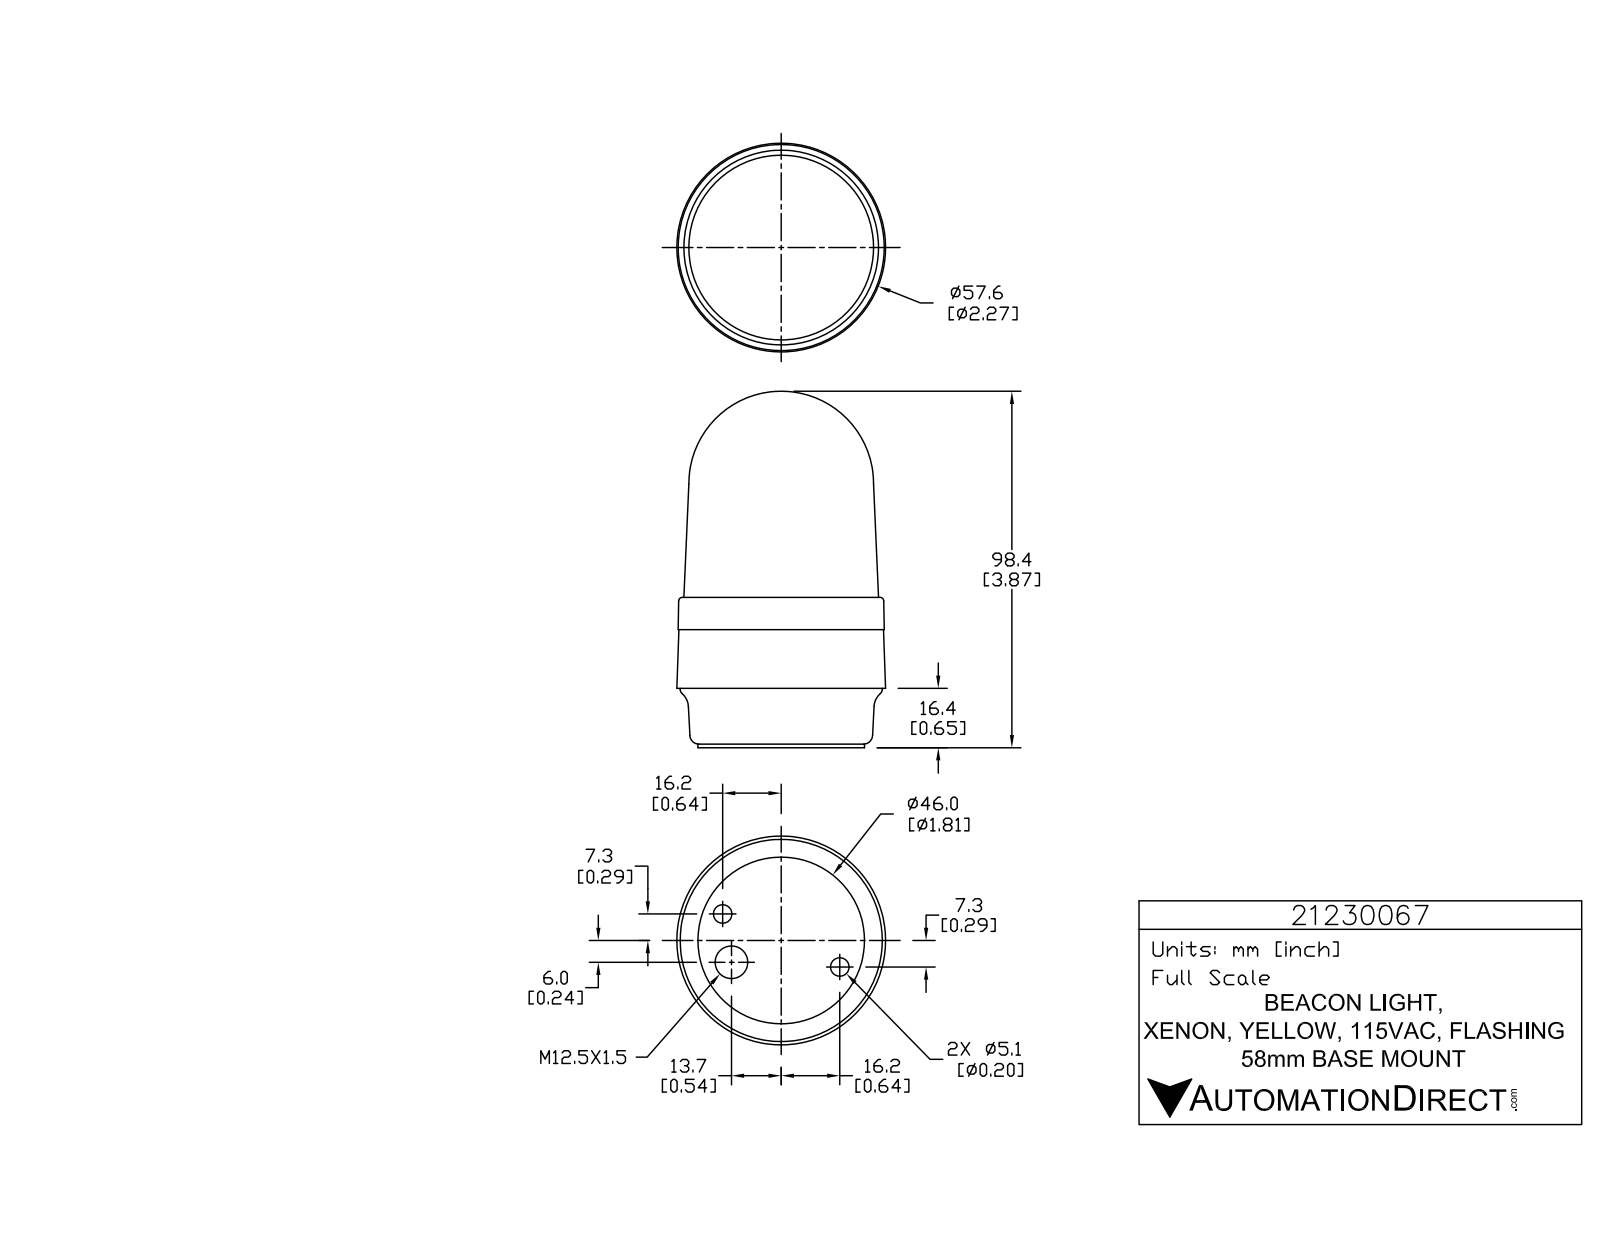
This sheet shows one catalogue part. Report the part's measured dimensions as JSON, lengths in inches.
{"part_name": "21230067", "step_written_by": "SolidWorks 2015 (AUTOMOTIVE_DESIGN)", "units": "inches", "bodies": {"solids": 1, "faces": 764, "planar": 527, "cylindrical": 145, "other": 92}, "overall_size": [3.874, 2.269, 2.269], "volume_in3": 12.2, "surface_area_in2": 29.33, "round_holes": [[0.039, 3], [0.201, 2], [0.354, 1]], "round_bosses_or_shafts": [[0.226, 3], [0.056, 3], [2.197, 1], [1.811, 1]], "partial_cylinders_radius": [[0.008, 6], [0.008, 6], [0.008, 6], [0.131, 6], [0.004, 3], [0.005, 3], [0.007, 3], [0.008, 3]], "face_to_face_distances": [0.646, 0.039, 0.606, 1.634, 1.594, 0.988, 1.283, 1.244, 0.638, 0.35], "hole_center_spacings": [0.534, 1.179, 1.398]}
